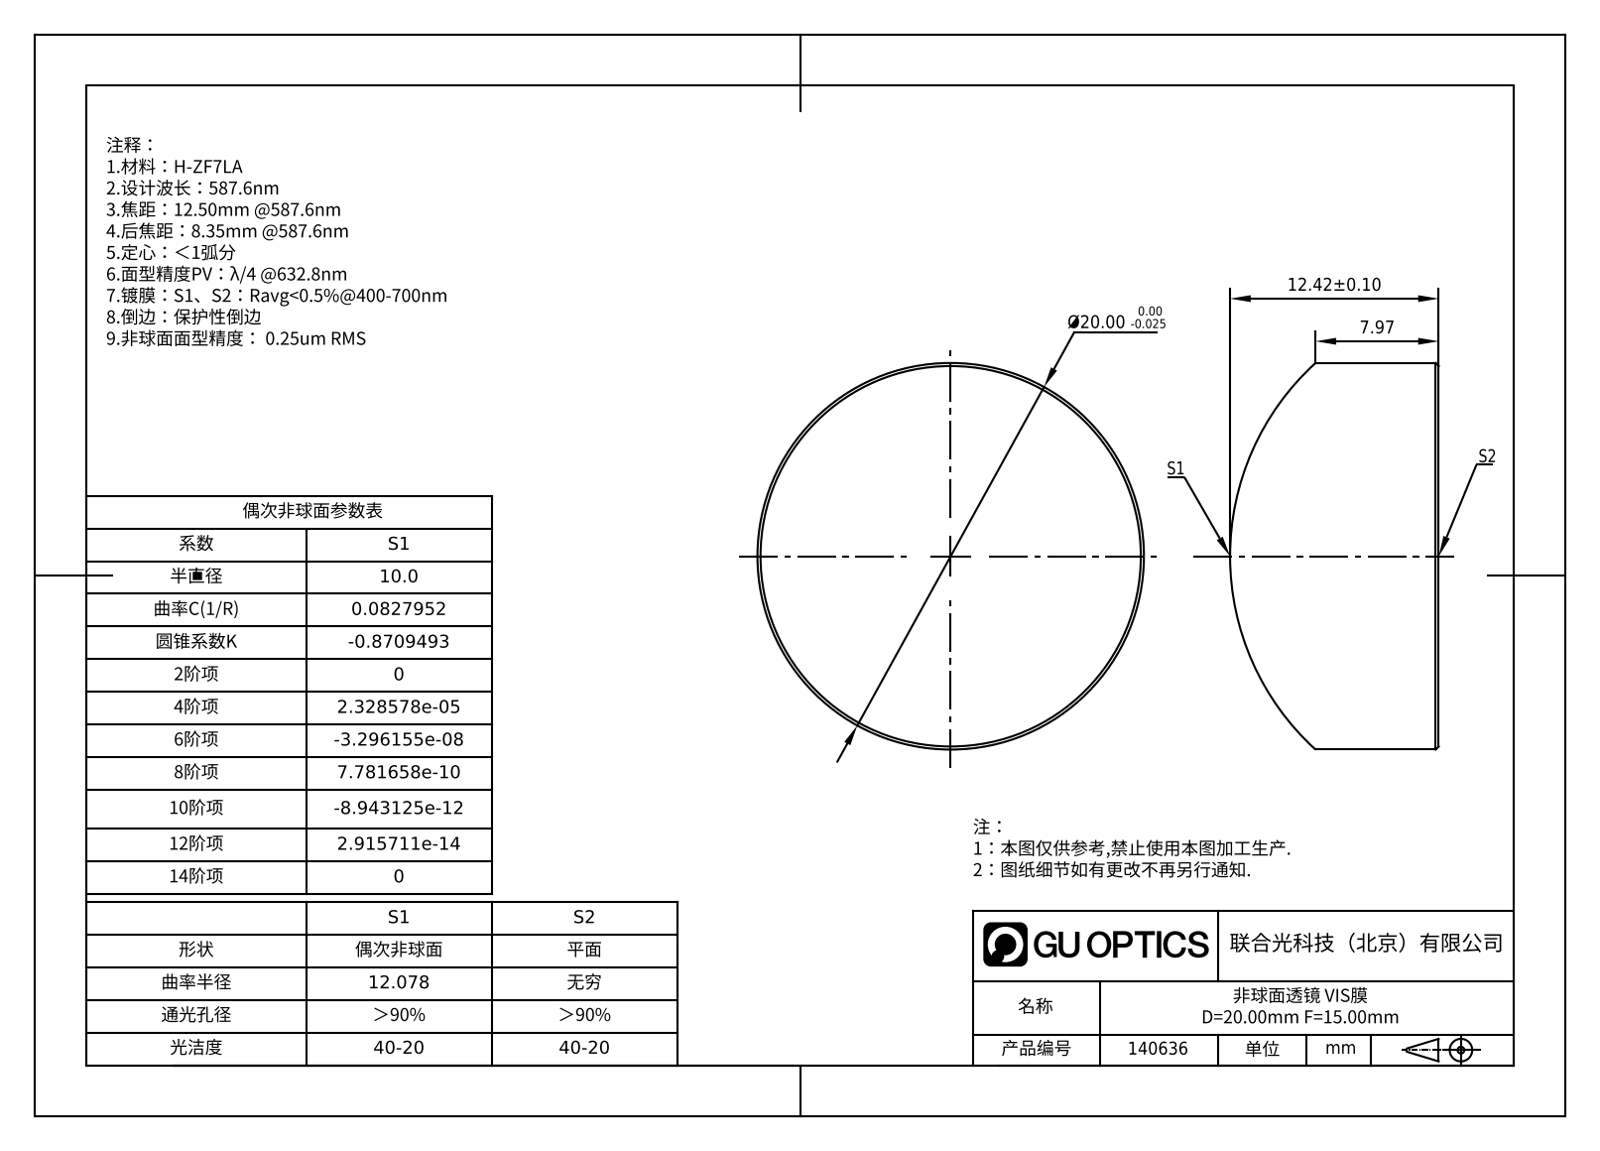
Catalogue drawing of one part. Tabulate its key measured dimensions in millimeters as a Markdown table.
| quantity | value |
| --- | --- |
| part name | GLA11-020-015-H-VIS |
| STEP written by | SolidWorks 2022 (AUTOMOTIVE_DESIGN) |
| units | millimeters |
| bodies | 1 solid, 7 faces (1 planar, 2 cylindrical, 4 other) |
| overall size | 20 × 20 × 12.42 |
| volume | 3 248 mm³ |
| surface area | 1 184 mm² |
| round bosses / shafts (diameter × count) | 20 × 1 |
